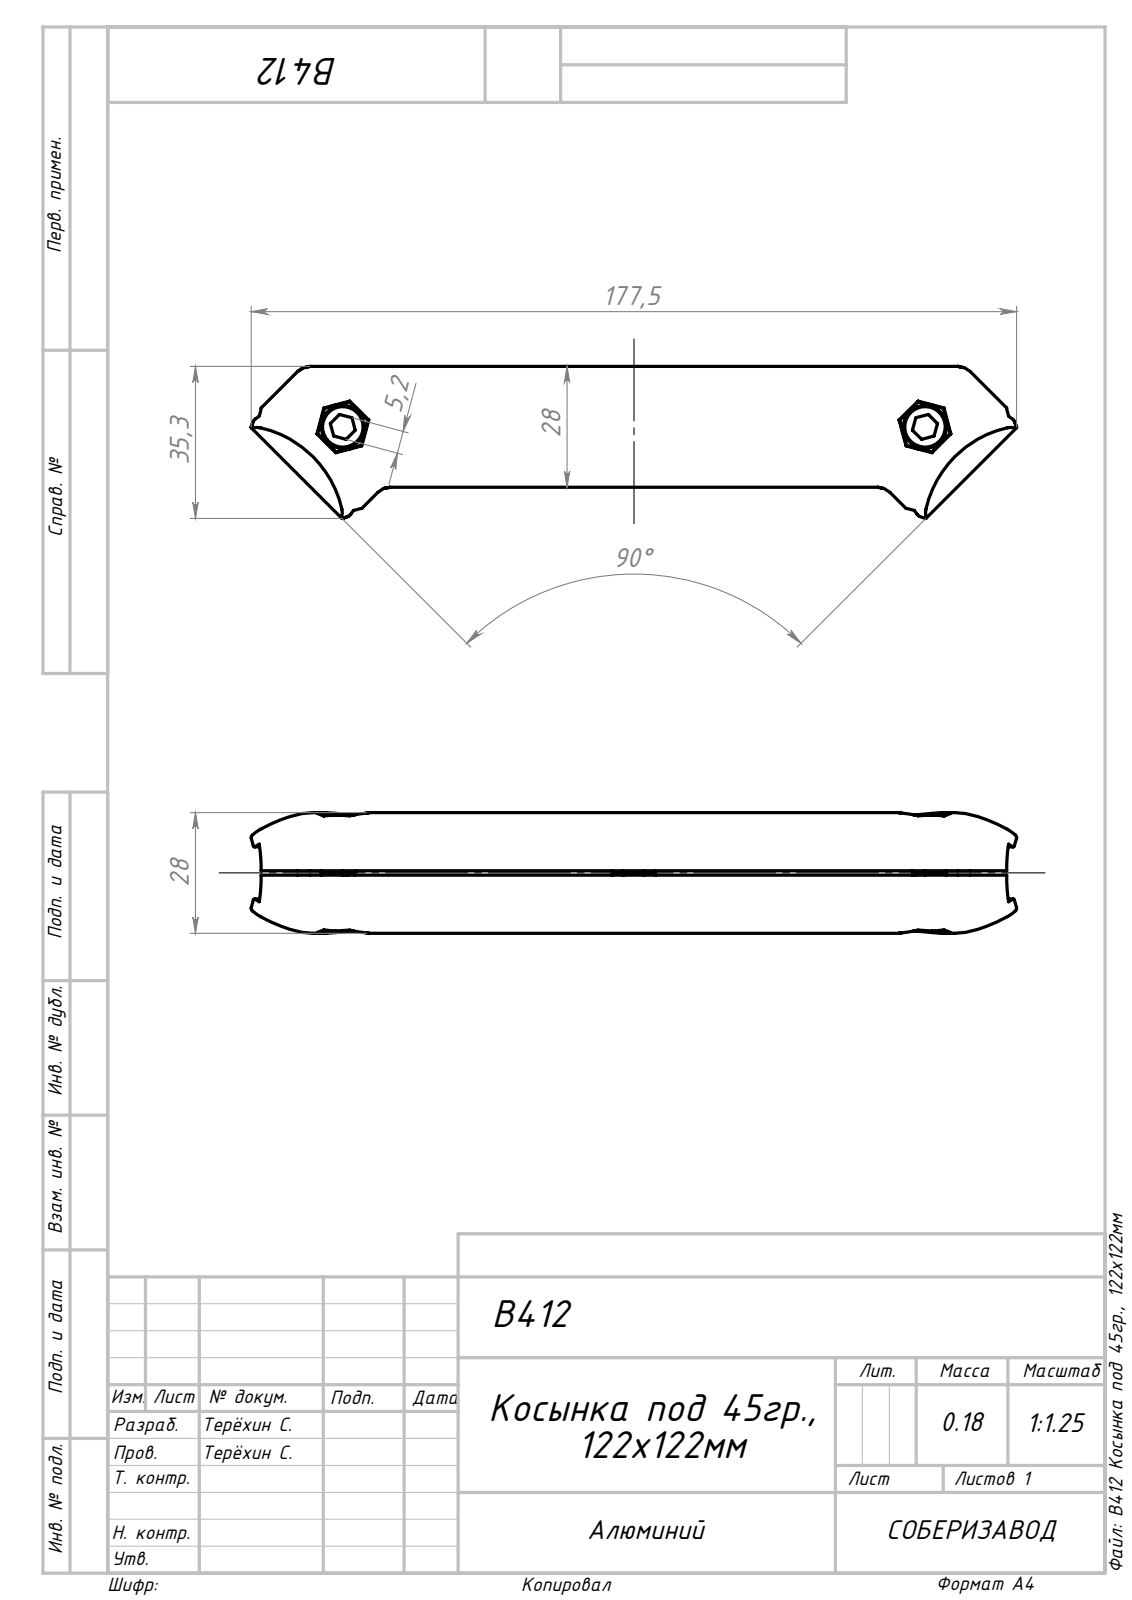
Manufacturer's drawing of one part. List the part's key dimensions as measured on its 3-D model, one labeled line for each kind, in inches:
Part name (STEP PRODUCT): M6-L7-LUO-MAO.stp_00; Косынка под 45гр., 122х122мм, B412.stp_00; M6X25-LUO-SHI.stp_00; Сборка3 (+1 more)
STEP written by: SolidWorks 2022 (AUTOMOTIVE_DESIGN)
Units: inches
Bodies: 6 solids, 524 faces (162 planar, 196 cylindrical, 166 other)
Overall size (bounding box): 6.989 × 1.389 × 1.102
Volume: 3.923 in³ · Surface area: 63.73 in²
Round holes (diameter × count): ⌀0.205 ×2, ⌀0.256 ×2
Round bosses / shafts (diameter × count): ⌀0.394 ×2, ⌀0.236 ×2
Partial cylindrical surfaces — rounded edges, fillets, slot ends (radius × count): R0.984 ×18, R0.157 ×12, R0.886 ×10, R0.02 ×8, R0.49 ×2, R0.559 ×2
Main face-to-face distances: 0.196, 0.039, 0.098, 1.969, 0.276, 0.236, 0.512, 0.405, 0.366, 2.066
Hole centre spacings: 5.315
